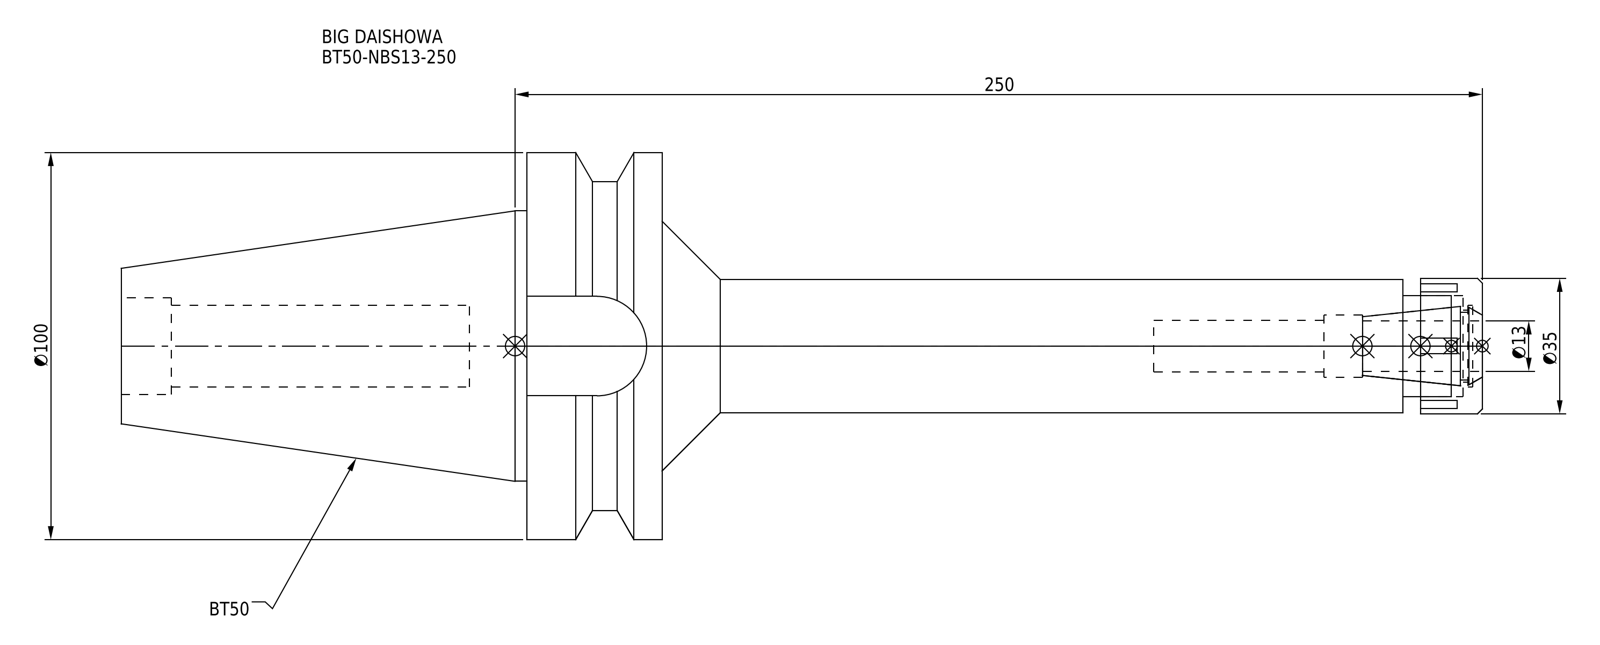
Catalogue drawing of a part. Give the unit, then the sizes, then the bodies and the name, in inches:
Units: inches
Overall size (bounding box): 13.85 × 3.937 × 3.937
Round holes (diameter × count): ⌀0.524 ×1, ⌀0.63 ×1, ⌀0.728 ×1, ⌀0.827 ×1, ⌀0.835 ×1, ⌀0.984 ×1, ⌀1.024 ×1
Round bosses / shafts (diameter × count): ⌀3.937 ×1, ⌀3.346 ×1, ⌀2.75 ×1, ⌀1.378 ×1, ⌀1.358 ×1
Partial cylindrical surfaces — rounded edges, fillets, slot ends (radius × count): R0.506 ×1
Main face-to-face distances: 1.378, 5.504, 4.126, 2.787, 8.346, 9.724, 13.85, 0.807, 0.315, 1.012
Volume: 40.01 in³ · Surface area: 125.1 in²
Bodies: 2 solids, 89 faces (45 planar, 30 cylindrical, 14 other)
Part name (STEP PRODUCT): DXF_TEMP_ASSY_ASM_4_ASM.stp; BT50-NBS13-250; BT50-NBS13-250.stp; NBN13_1.stp (+3 more)
STEP written by: SolidWorks 2019 (CONFIG_CONTROL_DESIGN)
